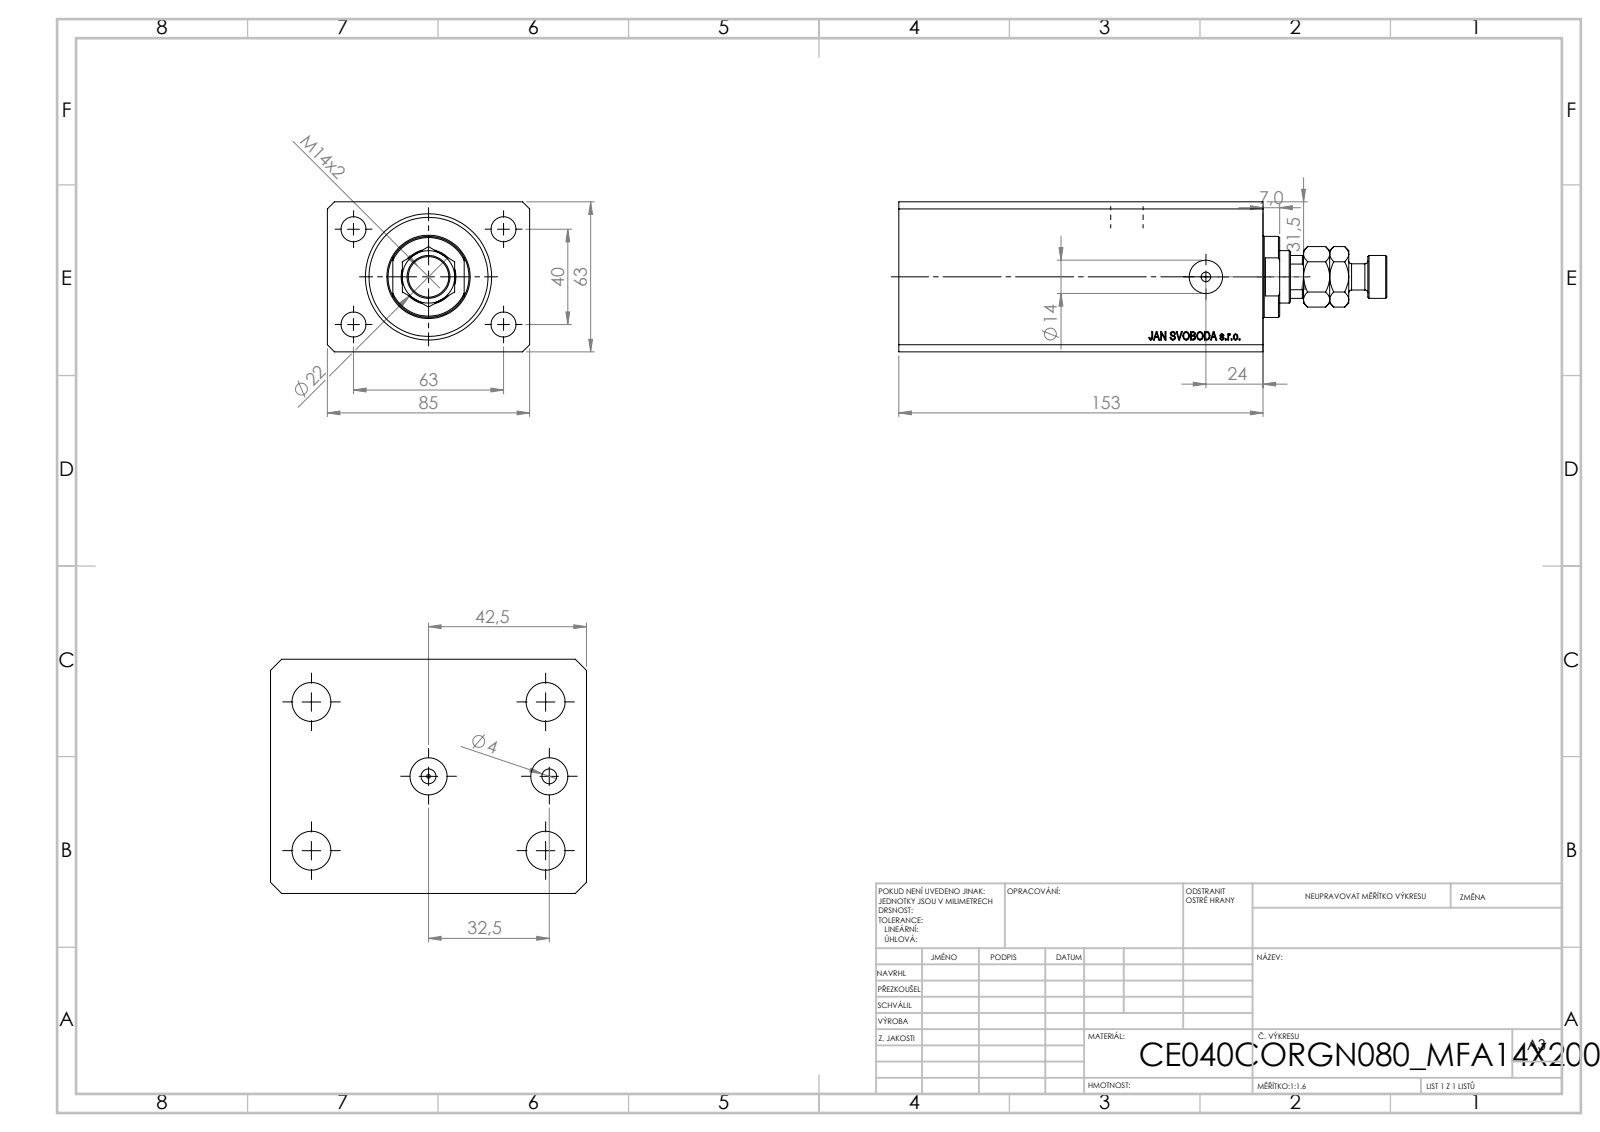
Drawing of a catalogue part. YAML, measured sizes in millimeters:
part_name: "V250CE_VC_C; V250CE_C_VCP; MFA; V250CE_C_Body"
step_written_by: "SolidWorks 2019 (CONFIG_CONTROL_DESIGN)"
units: millimeters
bodies: {solids: 4, faces: 920, planar: 444, cylindrical: 50, other: 426}
overall_size: [205, 85, 63]
volume: 707105
surface_area: 124322
round_holes:
  - {diameter: 4, count: 4}
  - {diameter: 10.5, count: 4}
  - {diameter: 10, count: 2}
  - {diameter: 14, count: 2}
  - {diameter: 1.25, count: 1}
  - {diameter: 12.5, count: 1}
  - {diameter: 22, count: 1}
  - {diameter: 40, count: 1}
  - {diameter: 53, count: 1}
round_bosses_or_shafts:
  - {diameter: 34, count: 1}
  - {diameter: 18, count: 1}
  - {diameter: 11, count: 1}
partial_cylinders:
  - {radius: 10.5, count: 1}
face_to_face_distances: [63, 85, 153, 17, 136, 11.4, 124.6, 141.6, 100.4, 80]
hole_center_spacings: [37.31, 20.02, 40, 63, 67.05, 74.63, 32.5, 105]
